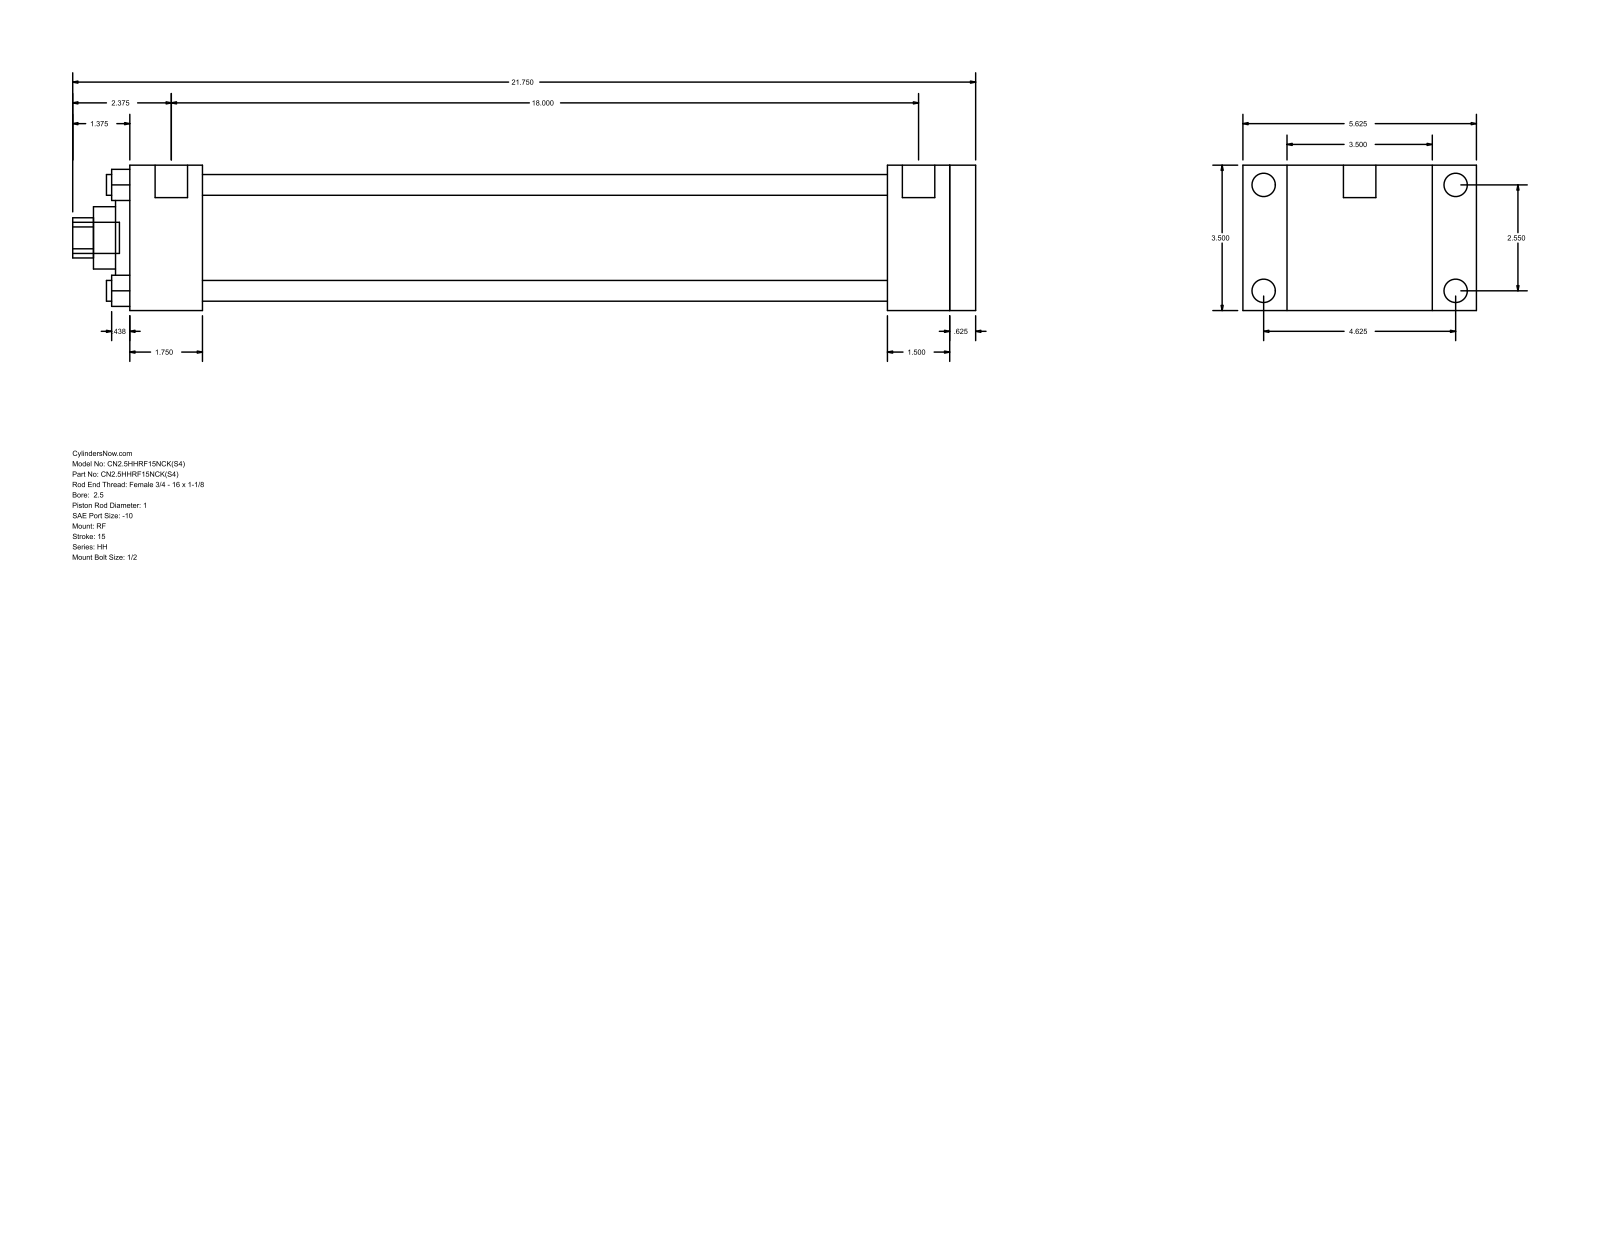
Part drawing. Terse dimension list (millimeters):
name: HH_RF__0250_1
written by: GSSL Pune (CONFIG_CONTROL_DESIGN)
unit: mm
bodies: 0 solids, 94 faces (65 planar, 29 cylindrical, 0 other)
size: 552.45 × 142.88 × 88.9
holes: 4× ⌀12.7, 1× ⌀25.4, 1× ⌀38.1, 1× ⌀60.33, 1× ⌀73.03
bosses: 4× ⌀14.3, 4× ⌀5.56, 2× ⌀19.84, 1× ⌀19.05
rounds: 1× R12.29
face distances: 88.9, 15.87, 501.66, 517.53, 44.46, 457.2, 473.07, 463.56, 419.1, 38.1
hole spacings: 45.79, 64.76, 91.58
